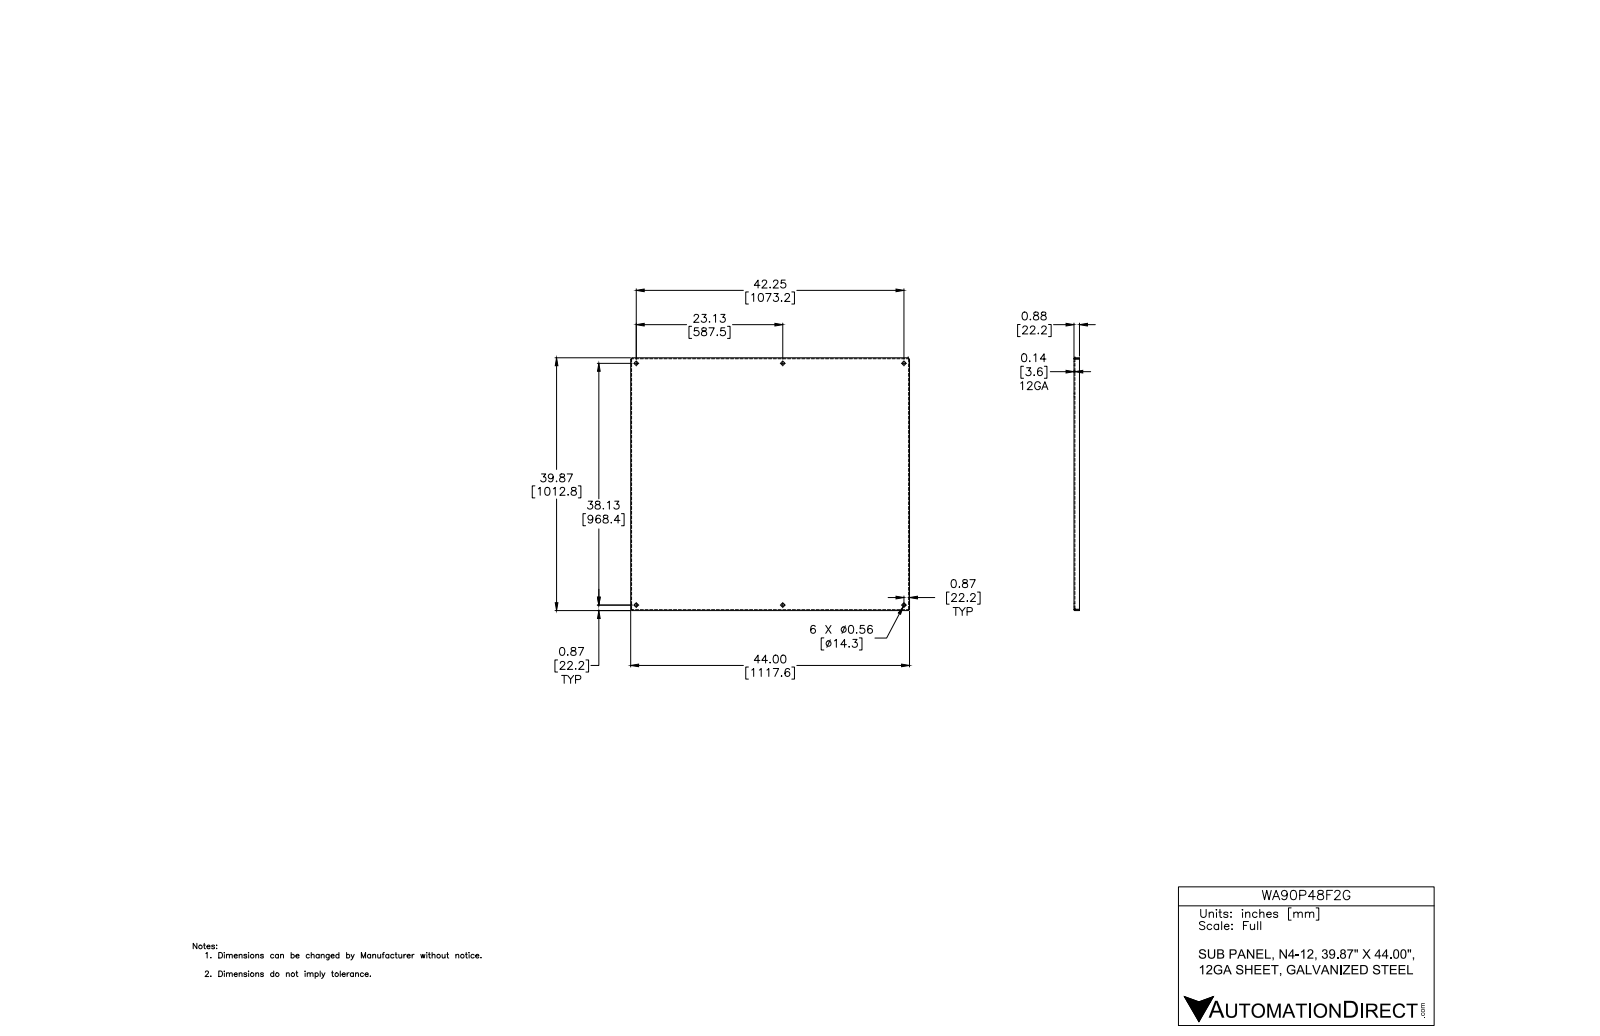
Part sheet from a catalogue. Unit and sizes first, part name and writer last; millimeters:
Units: millimetres
Overall size (bounding box): 1117.6 × 1013.2 × 22.2
Round holes (diameter × count): ⌀14.3 ×6
Partial cylindrical surfaces — rounded edges, fillets, slot ends (radius × count): R0.4 ×4, R3.6 ×4
Main face-to-face distances: 3.2, 1010, 3.2, 1114.4, 1013.2, 1006.8, 1117.6, 1111.3, 19.1, 22.2
Hole centre spacings: 536.6, 536.6, 968.7, 1073.2, 1107.4, 1107.4, 1445.7, 968.7
Volume: 3 836 000 mm³ · Surface area: 2 431 000 mm²
Bodies: 1 solid, 44 faces (22 planar, 14 cylindrical, 8 other)
Part name (STEP PRODUCT): WA_P_F_G
STEP written by: Autodesk Inventor 2012 (AUTOMOTIVE_DESIGN)
